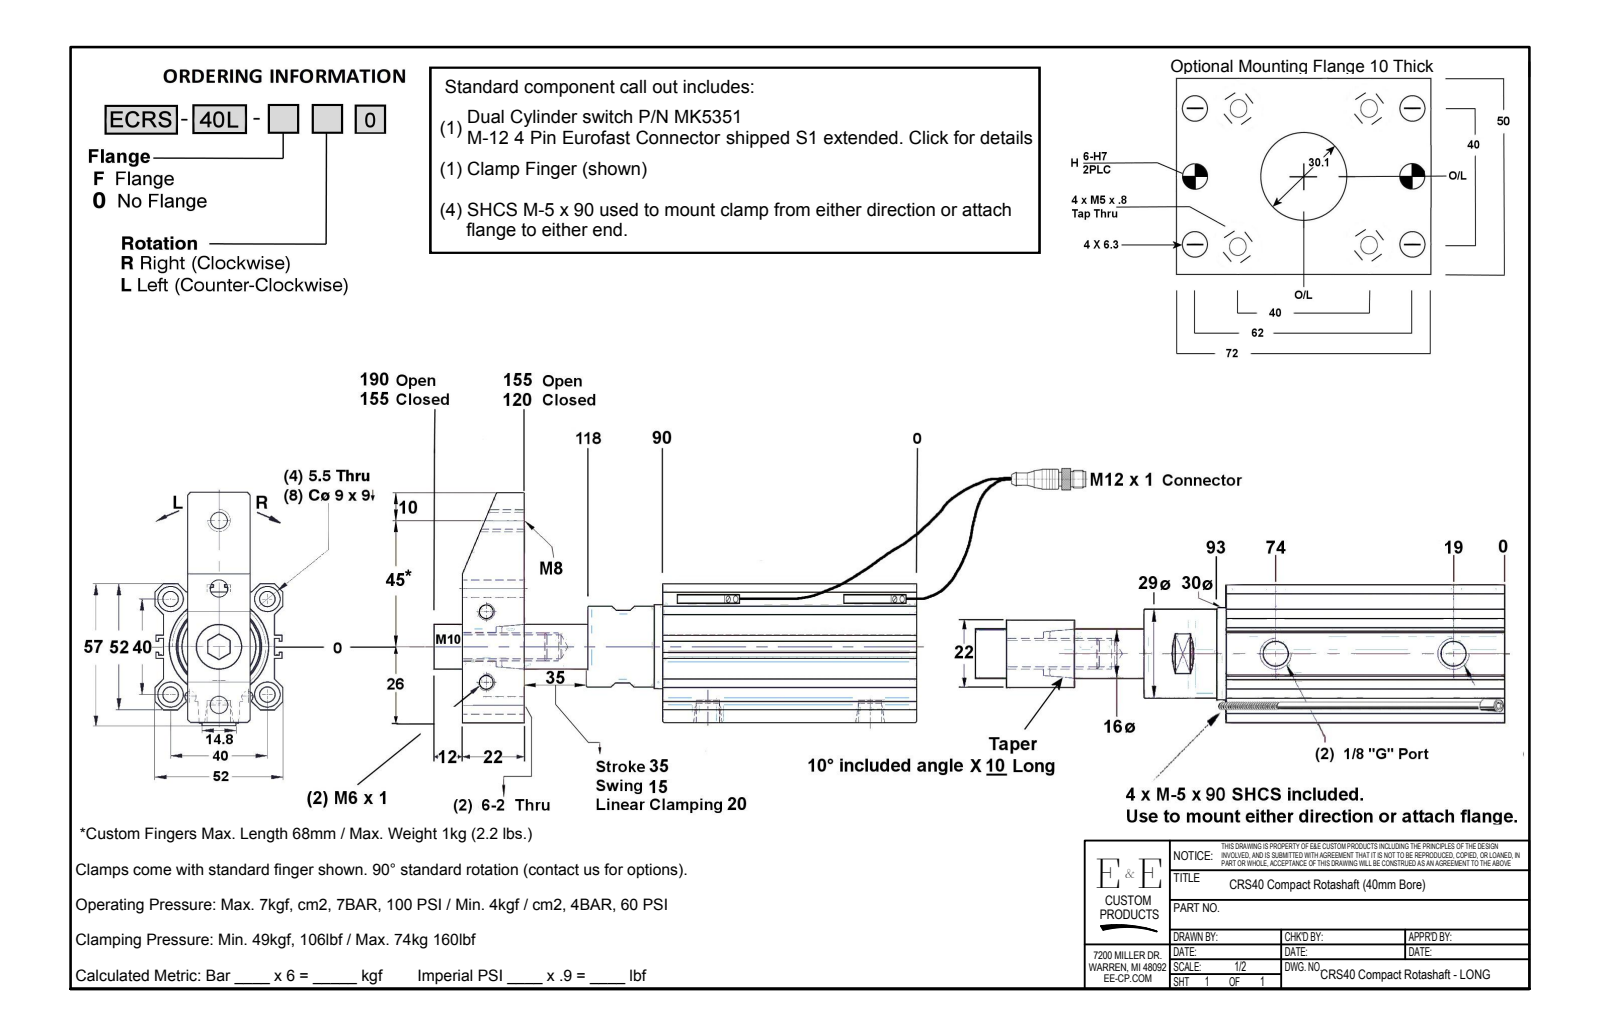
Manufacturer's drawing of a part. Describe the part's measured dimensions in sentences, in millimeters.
The part is named "CRS40 COMPACT ROTASHAFT". Its 3-D file was written by "Autodesk Inventor 2018 (AUTOMOTIVE_DESIGN)". It is 7 solids with 486 faces: 143 planar, 185 cylindrical and 158 other. Overall it measures 151.5 by 87.2 by 52 millimeters. Its volume is 205 320 cubic millimeters and its surface area 78 055 square millimeters. Round holes: 4 of diameter 5.5, 4 of diameter 9, 2 of diameter 2, 2 of diameter 5, 2 of diameter 6, 2 of diameter 6.2, 2 of diameter 6.8, 2 of diameter 7, 2 of diameter 8.2, 1 of diameter 10.5, 1 of diameter 11.62, 1 of diameter 16. Round bosses or shafts: 2 of diameter 13, 2 of diameter 8.7, 1 of diameter 44, 1 of diameter 30, 1 of diameter 29, 1 of diameter 18, 1 of diameter 16, 1 of diameter 10. Partial cylindrical surfaces (rounded edges, fillets, slot ends): 2 of radius 2, 1 of radius 22.43, 1 of radius 34.5. The main face-to-face distances are 49, 3, 12, 15, 34, 22, 52, 37, 57, 46. The hole center spacings are 28.28, 40, 20.01, 20.02, 28.25, 28.32, 32.02, 45.35.
